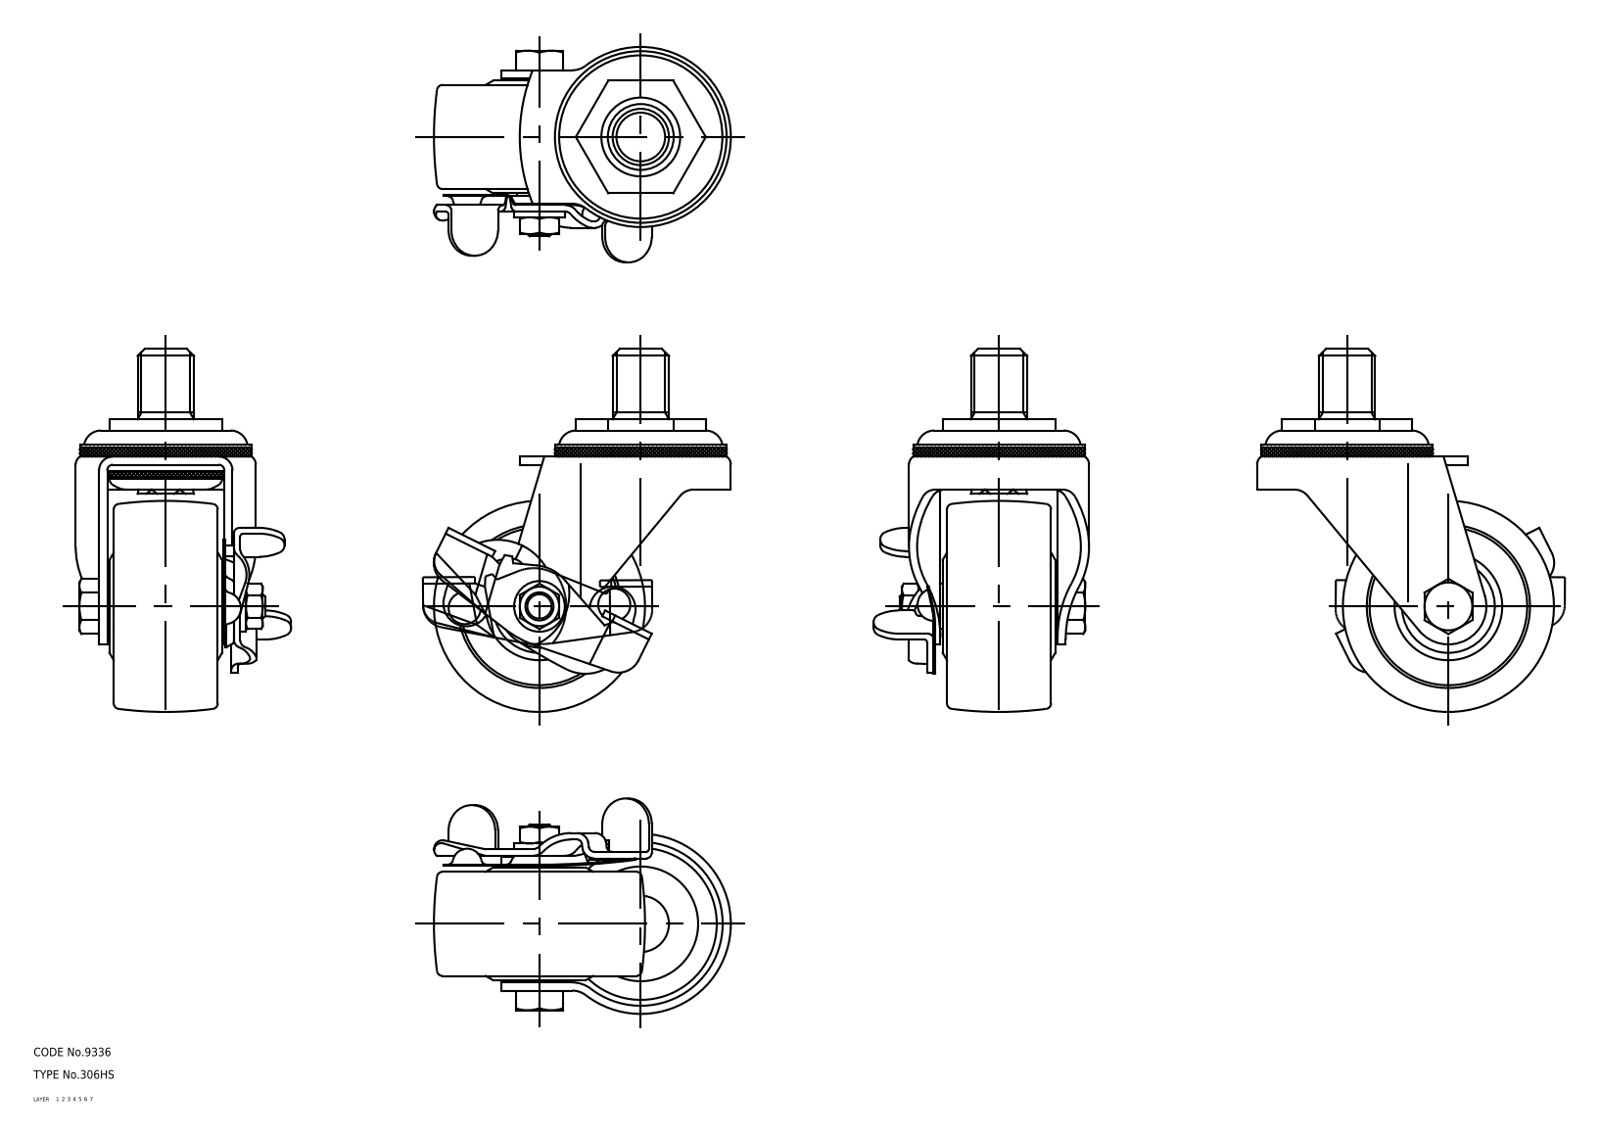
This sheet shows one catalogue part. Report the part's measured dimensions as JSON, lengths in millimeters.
{"part_name": "67131051; 67131064; 67131077; 67131090 (+2 more)", "step_written_by": "CADfix (AUTOMOTIVE_DESIGN)", "units": "millimeters", "bodies": {"solids": 6, "faces": 360, "planar": 0, "cylindrical": 0, "other": 360}, "overall_size": [129, 105.58, 76.56], "volume_mm3": 236665, "surface_area_mm2": 62447}
